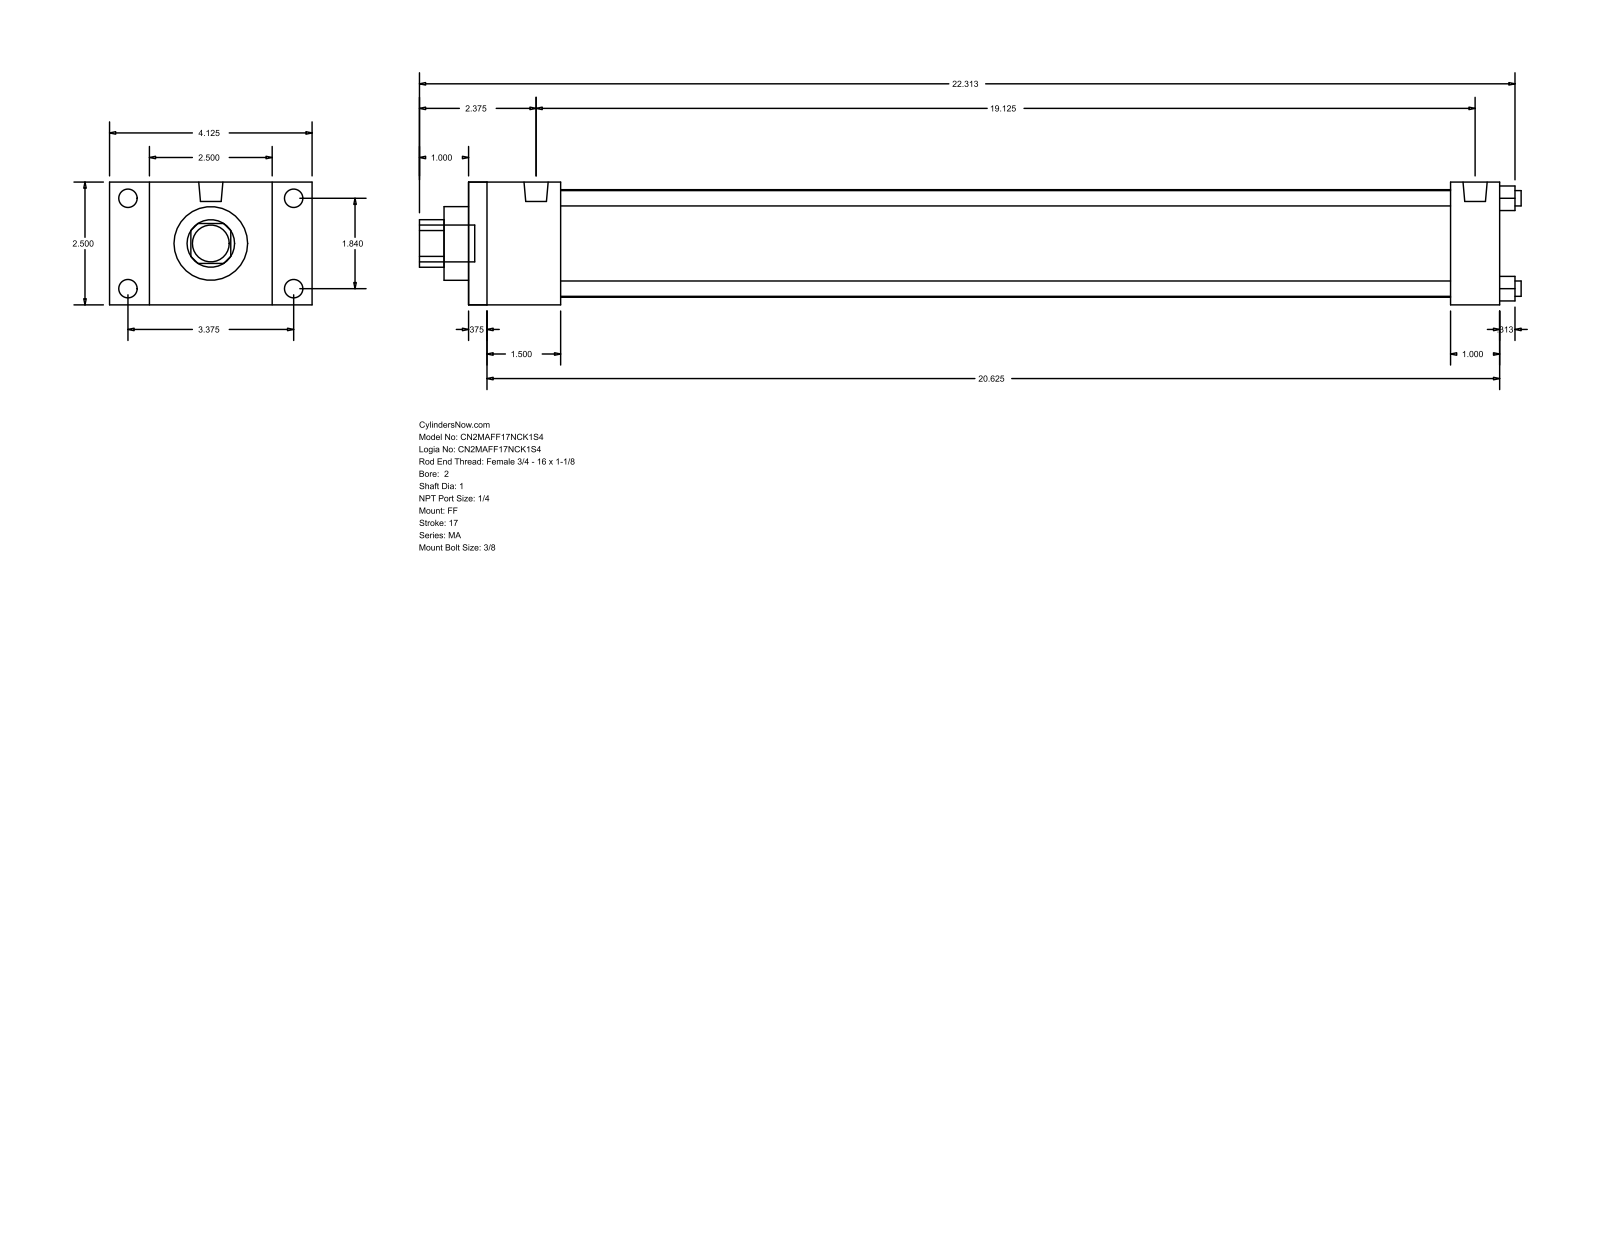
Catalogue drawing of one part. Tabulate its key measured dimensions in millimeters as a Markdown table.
| quantity | value |
| --- | --- |
| part name | MA_FF__0200_1 |
| STEP written by | GSSL Pune (CONFIG_CONTROL_DESIGN) |
| units | millimeters |
| bodies | 0 solids, 92 faces (64 planar, 28 cylindrical, 0 other) |
| overall size | 569.91 × 104.78 × 63.5 |
| round holes (diameter × count) | 7.94 × 4, 25.4 × 1, 38.1 × 1, 55.63 × 1 |
| round bosses / shafts (diameter × count) | 9.53 × 4, 7.94 × 4, 12.49 × 2, 19.05 × 1 |
| partial cylindrical surfaces (radius × count) | 12.29 × 1 |
| main face-to-face distances | 63.5, 533.4, 9.52, 523.88, 25.4, 20.64, 12.7, 47.63, 508, 38.11 |
| hole center spacings | 33.05, 46.74, 66.1 |
